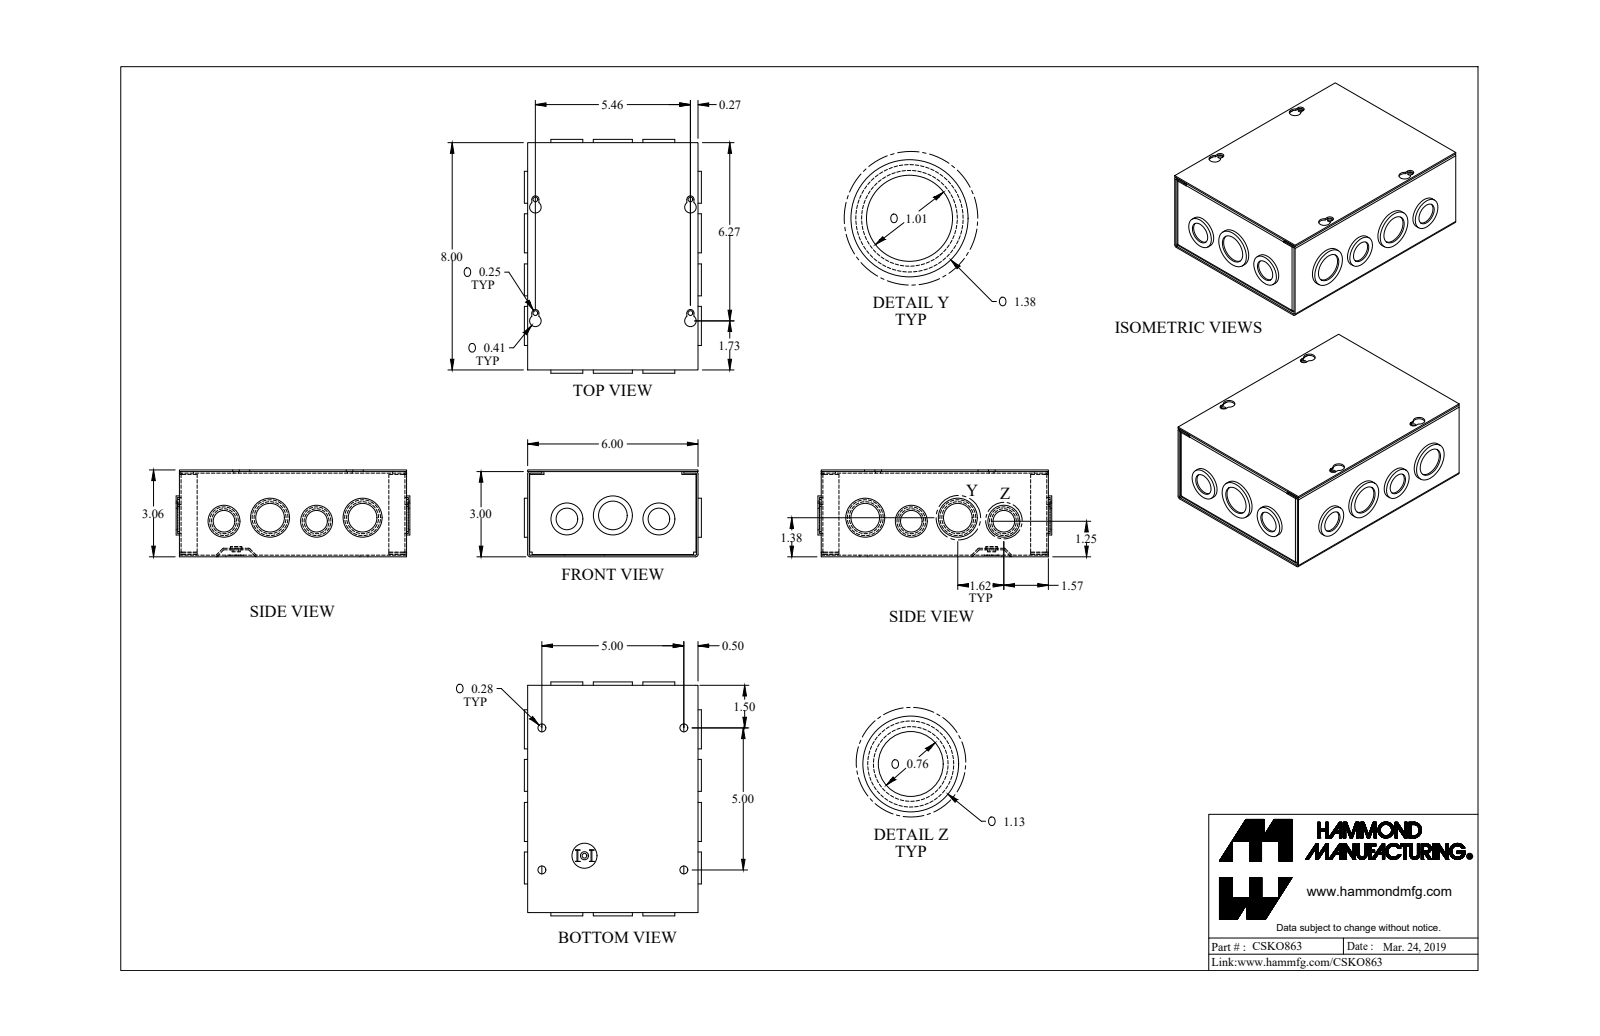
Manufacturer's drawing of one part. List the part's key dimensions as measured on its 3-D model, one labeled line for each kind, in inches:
Part name (STEP PRODUCT): CSKO863_Default
STEP written by: SolidWorks 2019 (CONFIG_CONTROL_DESIGN)
Units: inches
Bodies: 4 solids, 373 faces (181 planar, 184 cylindrical, 8 other)
Overall size (bounding box): 8.234 × 6.234 × 3.057
Volume: 11.82 in³ · Surface area: 422.1 in²
Round holes (diameter × count): ⌀1.011 ×7, ⌀0.17 ×5, ⌀0.281 ×4, ⌀0.761 ×4, ⌀1.261 ×3, ⌀0.5 ×1
Round bosses / shafts (diameter × count): ⌀1.125 ×6, ⌀0.875 ×4, ⌀1.375 ×3, ⌀0.875 ×3, ⌀1.125 ×1, ⌀0.492 ×1, ⌀0.284 ×1
Partial cylindrical surfaces — rounded edges, fillets, slot ends (radius × count): R0.029 ×12, R0.086 ×12, R0.057 ×8, R0.125 ×4, R0.203 ×4
Main face-to-face distances: 0.057, 3, 2.943, 3.057, 5.943, 6, 7.943, 0.114, 8, 5.886
Hole centre spacings: 0.55, 1.625, 4.506, 5, 5.254, 6.9, 3.26, 4
